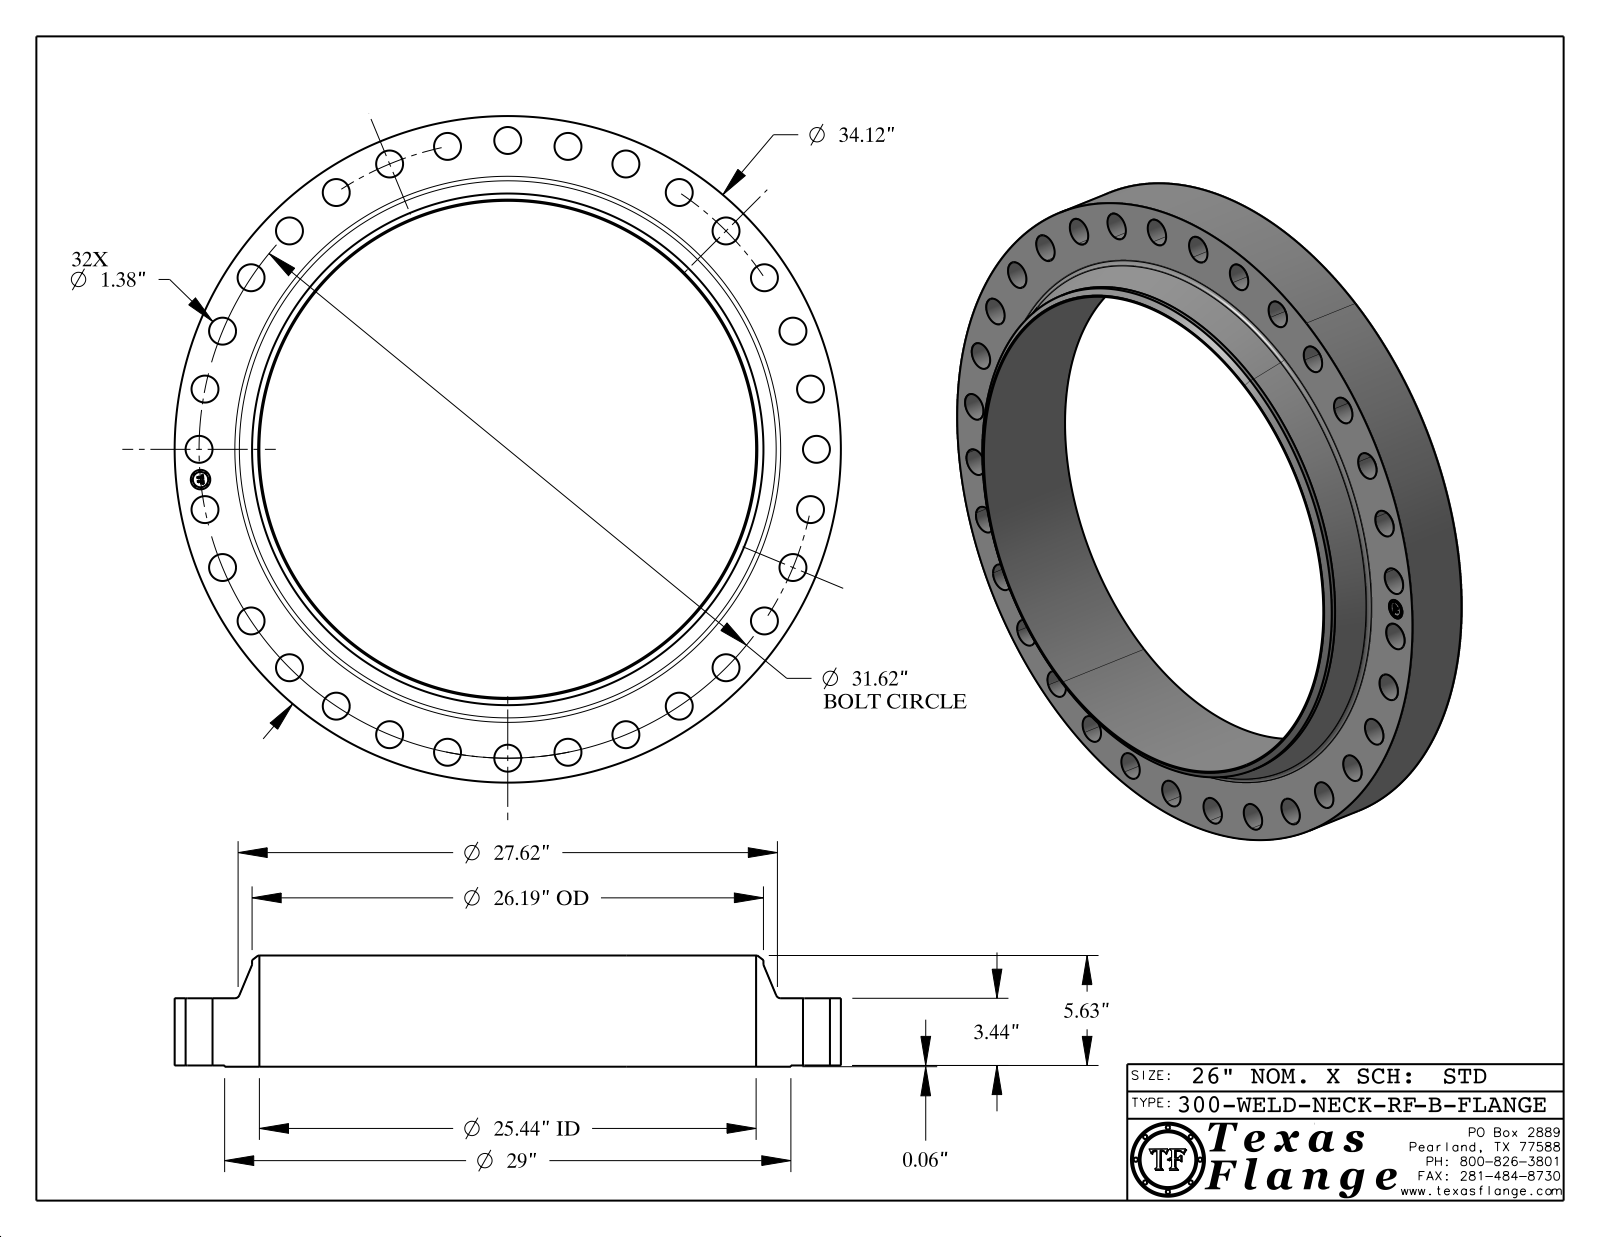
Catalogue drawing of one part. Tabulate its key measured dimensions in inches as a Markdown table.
| quantity | value |
| --- | --- |
| part name | 300-WELD-NECK-RF, Series B |
| STEP written by | CATIA V5 STEP AP214 (AUTOMOTIVE_DESIGN) |
| units | inches |
| bodies | 1 solid, 467 faces (369 planar, 92 cylindrical, 6 other) |
| overall size | 34.12 × 34.12 × 5.693 |
| volume | 1 357 in³ |
| surface area | 2 142 in² |
| round holes (diameter × count) | 1.38 × 32, 1 × 1, 25.44 × 1 |
| round bosses / shafts (diameter × count) | 0.061 × 8, 34.12 × 1, 29 × 1, 26.19 × 1, 0.788 × 1 |
| main face-to-face distances | 3.44, 0.063, 3.503, 5.693, 5.63, 2.19, 3.488, 3.425, 0.015, 2.205 |
| hole center spacings | 15.81, 6.169, 26.291, 31.468, 14.906, 27.887, 30.259, 20.059 |
